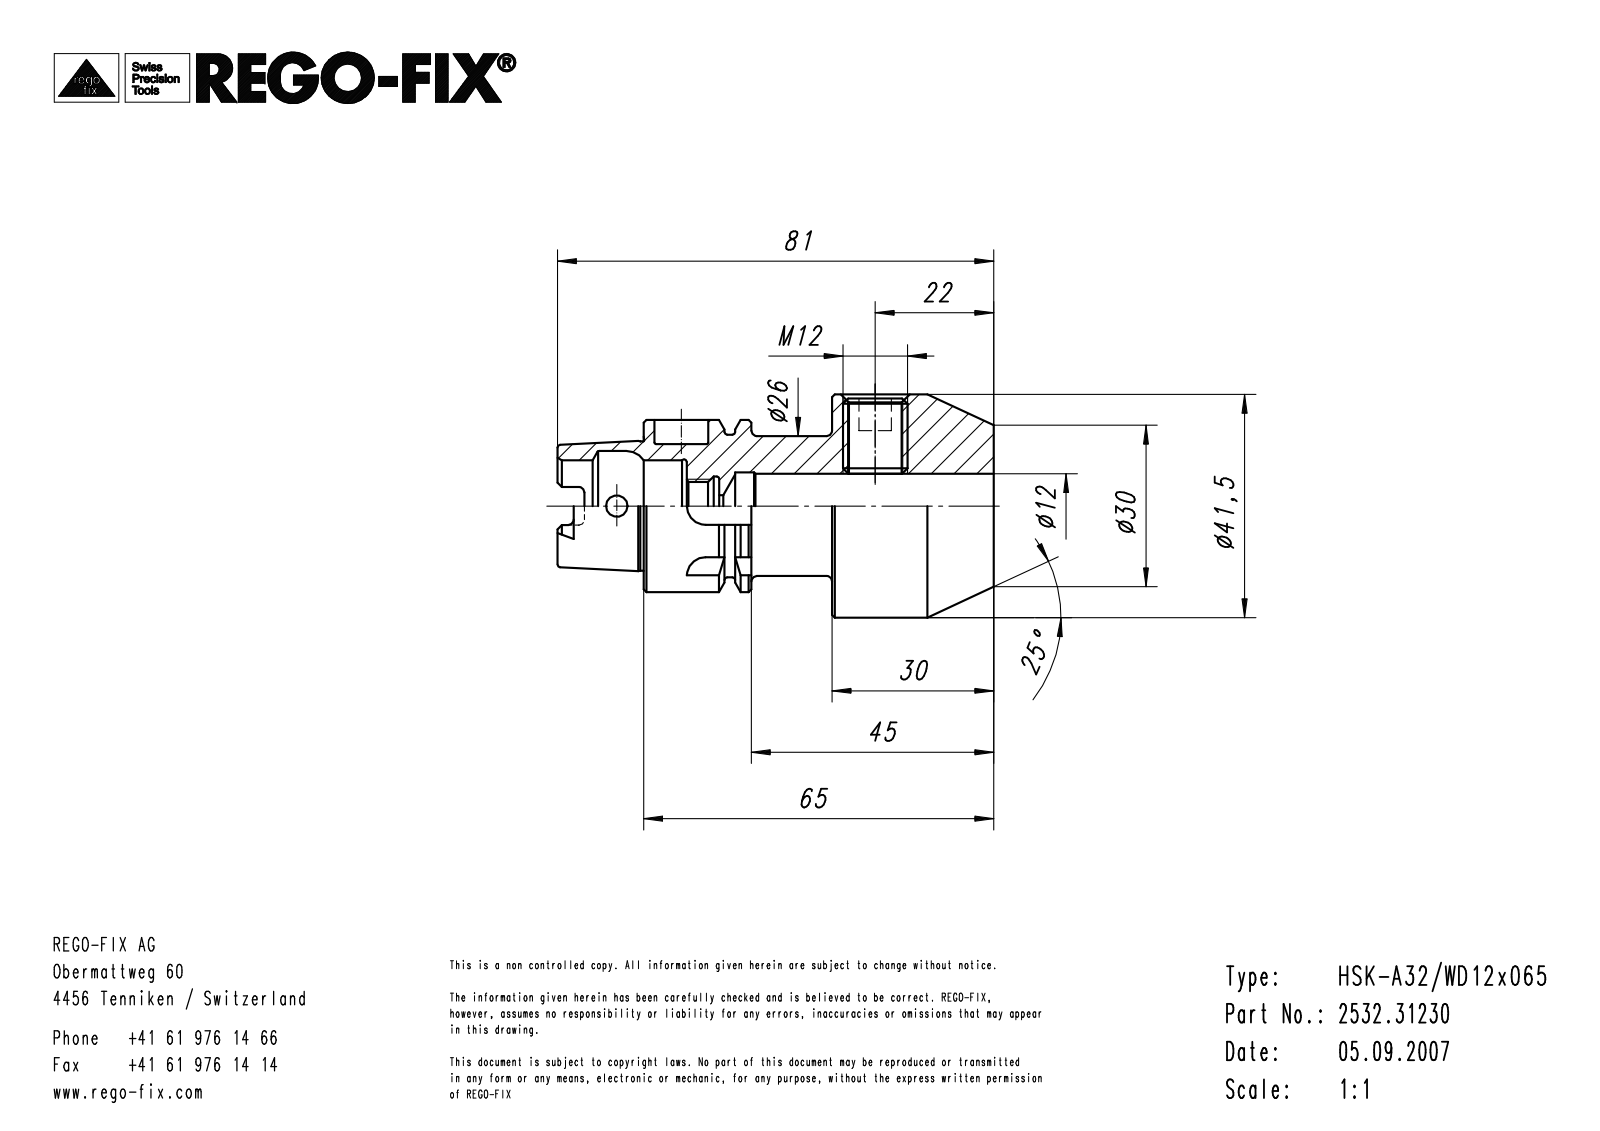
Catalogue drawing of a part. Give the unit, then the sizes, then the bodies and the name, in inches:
Units: inches
Overall size (bounding box): 3.268 × 1.654 × 1.654
Round holes (diameter × count): ⌀0.394 ×2, ⌀0.157 ×1, ⌀0.165 ×1, ⌀0.351 ×1, ⌀0.398 ×1, ⌀0.433 ×1, ⌀0.472 ×1, ⌀0.492 ×1, ⌀0.669 ×1, ⌀0.807 ×1
Round bosses / shafts (diameter × count): ⌀1.654 ×1, ⌀1.26 ×1, ⌀1.043 ×1, ⌀1.024 ×1, ⌀0.95 ×1
Partial cylindrical surfaces — rounded edges, fillets, slot ends (radius × count): R0.039 ×6, R0.054 ×4, R0.138 ×4
Main face-to-face distances: 1.26, 1.378, 2.638, 0.591, 0.787, 1.85, 0.315, 1.063, 0.079, 0.236
Hole centre spacings: 1.496
Volume: 3.351 in³ · Surface area: 23.91 in²
Bodies: 1 solid, 132 faces (49 planar, 36 cylindrical, 47 other)
STEP written by: Unknown (AUTOMOTIVE_DESIGN)
